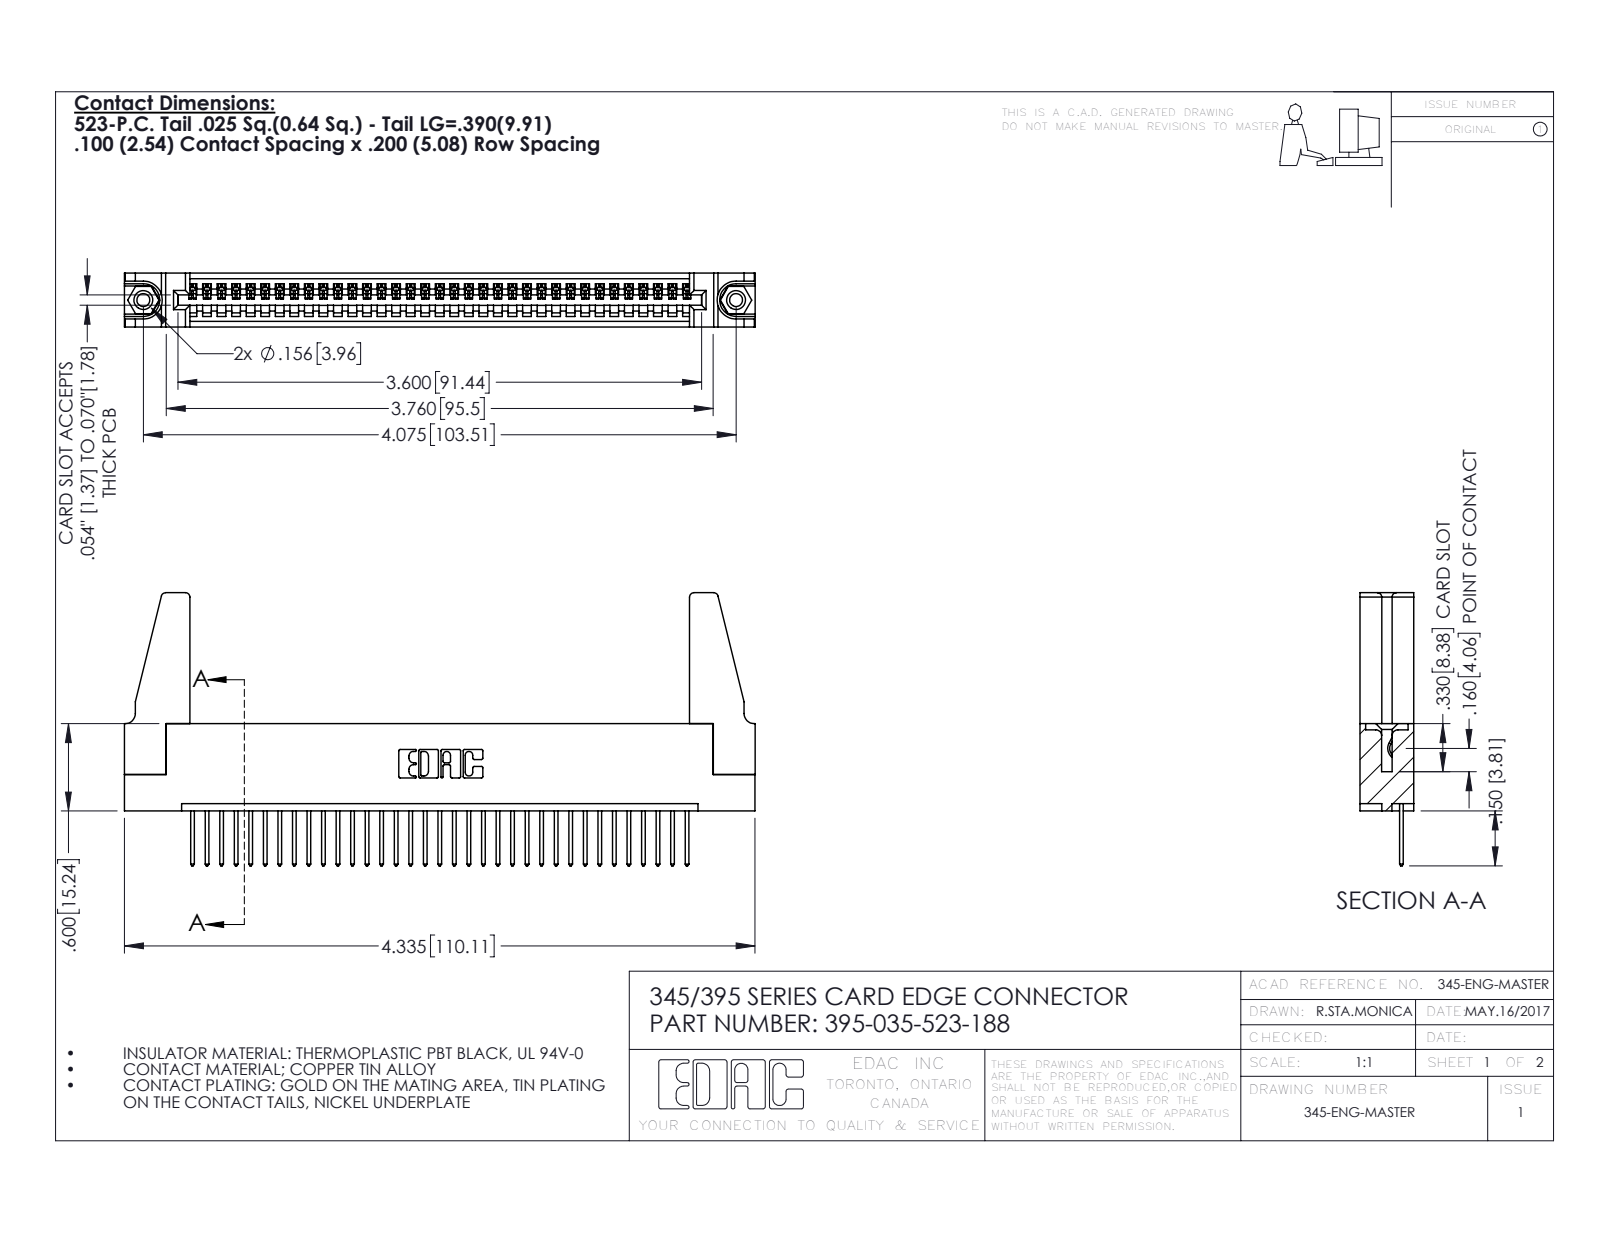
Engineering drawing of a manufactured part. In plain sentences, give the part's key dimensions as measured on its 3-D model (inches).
The part is named "395-035-523-188; 345-292-001_345-293-123; 345-220-078_345-220-088; 345-250-001_345-250-001-102 (+1 more)". Its 3-D file was written by "SolidWorks 2016 (CONFIG_CONTROL_DESIGN)". It is 40 solids with 2280 faces: 1552 planar, 712 cylindrical and 16 other. Overall it measures 4.336 by 1.877 by 0.37 inches. Its volume is 0.833 cubic inches and its surface area 26.16 square inches. Round holes: 2 of diameter 0.089, 2 of diameter 0.125, 2 of diameter 0.156, 1 of diameter 0.064. Round bosses or shafts: 2 of diameter 0.155. Partial cylindrical surfaces (rounded edges, fillets, slot ends): 70 of radius 0.006, 70 of radius 0.01, 22 of radius 0.01, 8 of radius 0.03, 6 of radius 0.007, 6 of radius 0.031, 3 of radius 0.026, 2 of radius 0.031. The main face-to-face distances are 0.072, 0.298, 0.37, 0.2, 0.098, 0.272, 0.025, 0.225, 0.149, 0.072. The hole center spacings are 0.27, 3.839, 4.075.
